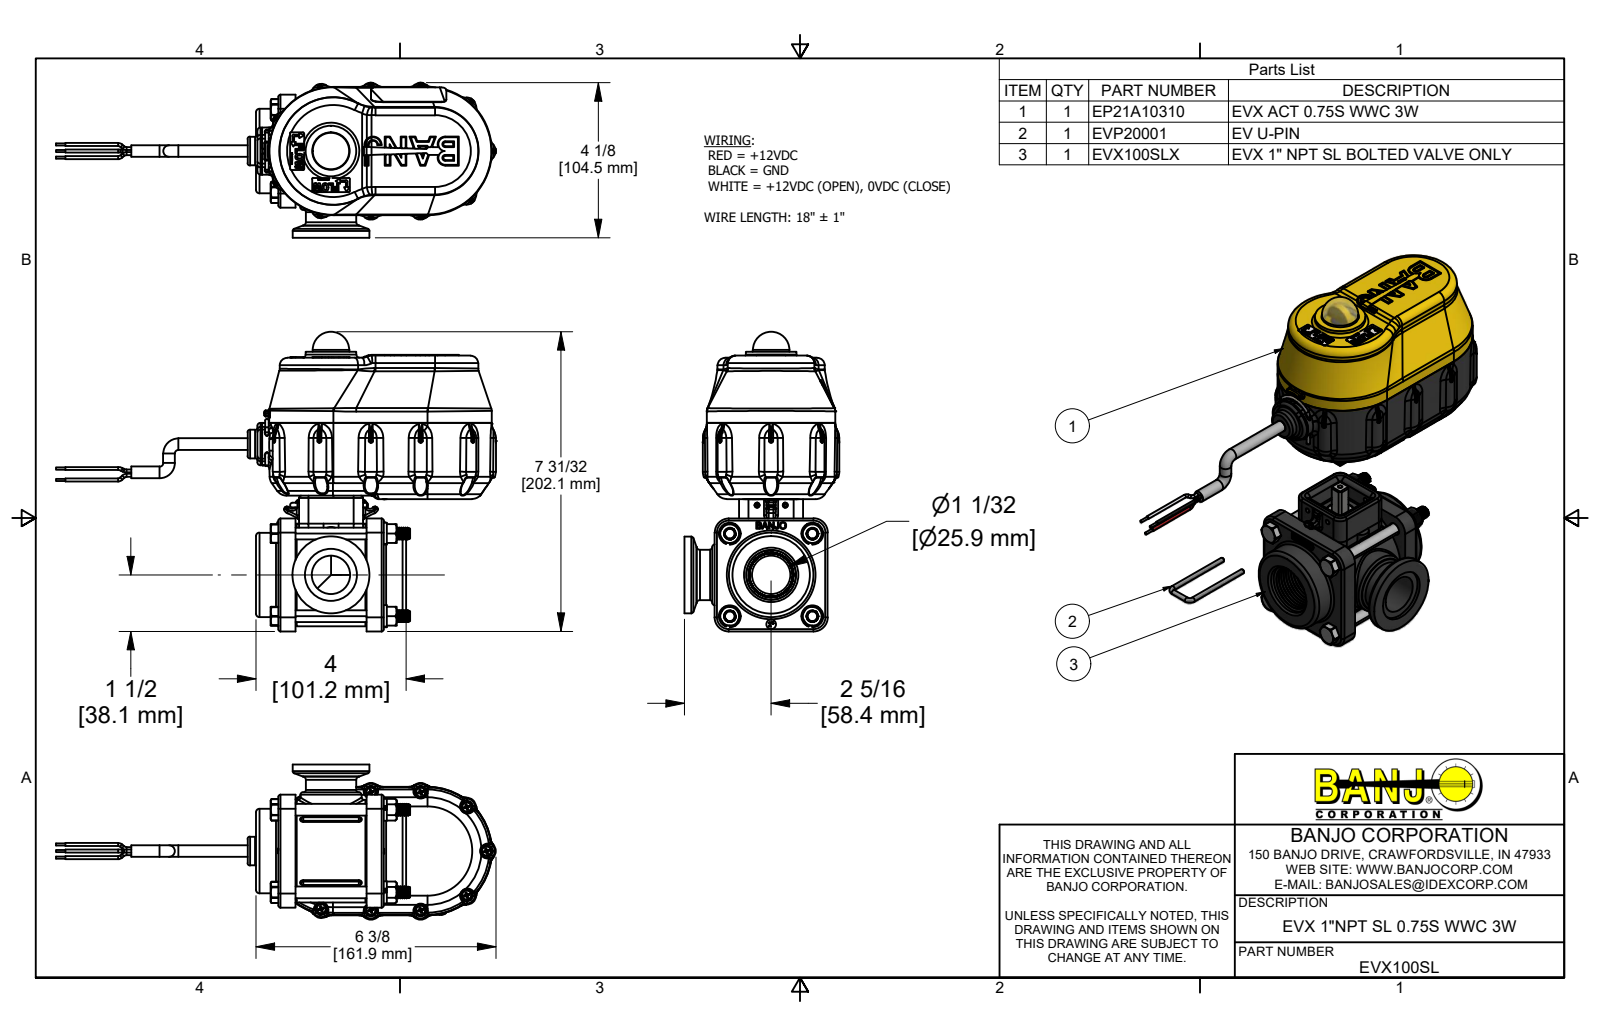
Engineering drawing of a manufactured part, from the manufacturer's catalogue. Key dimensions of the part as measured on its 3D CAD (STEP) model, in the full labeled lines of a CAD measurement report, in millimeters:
Part name (STEP PRODUCT): EVX100SL; EP21A10310; EP10310; IRF4905 (+8 more)
STEP written by: Autodesk Inventor 2019 (AUTOMOTIVE_DESIGN)
Units: millimetres
Bodies: 98 solids, 12101 faces (3290 planar, 3483 cylindrical, 5328 other)
Overall size (bounding box): 984.8 × 202.1 × 104.5
Volume: 862 000 mm³ · Surface area: 490 100 mm²
Round holes (diameter × count): ⌀2.4 ×11, ⌀3.8 ×11, ⌀2 ×7, ⌀2.7 ×4, ⌀3.2 ×4, ⌀3.5 ×4, ⌀3.8 ×4, ⌀3.8 ×4, ⌀4.3 ×4, ⌀6.4 ×4, ⌀8.2 ×4, ⌀8.9 ×4
Round bosses / shafts (diameter × count): ⌀6.8 ×60, ⌀6.4 ×17, ⌀2 ×15, ⌀3.6 ×11, ⌀2.7 ×11, ⌀2.2 ×11, ⌀1.5 ×6, ⌀8 ×5
Partial cylindrical surfaces — rounded edges, fillets, slot ends (radius × count): R0.3 ×180, R1 ×145, R0.3 ×84, R0.5 ×72, R1.5 ×58, R0.1 ×53, R0.8 ×38, R2 ×28
Main face-to-face distances: 2.5, 65.2, 1.4, 5.4, 1.5, 3.8, 11.7, 59.6, 3.2, 1.1
Hole centre spacings: 39.4, 55.7, 67.5, 26.6, 38.4, 42.2, 48, 68.3
